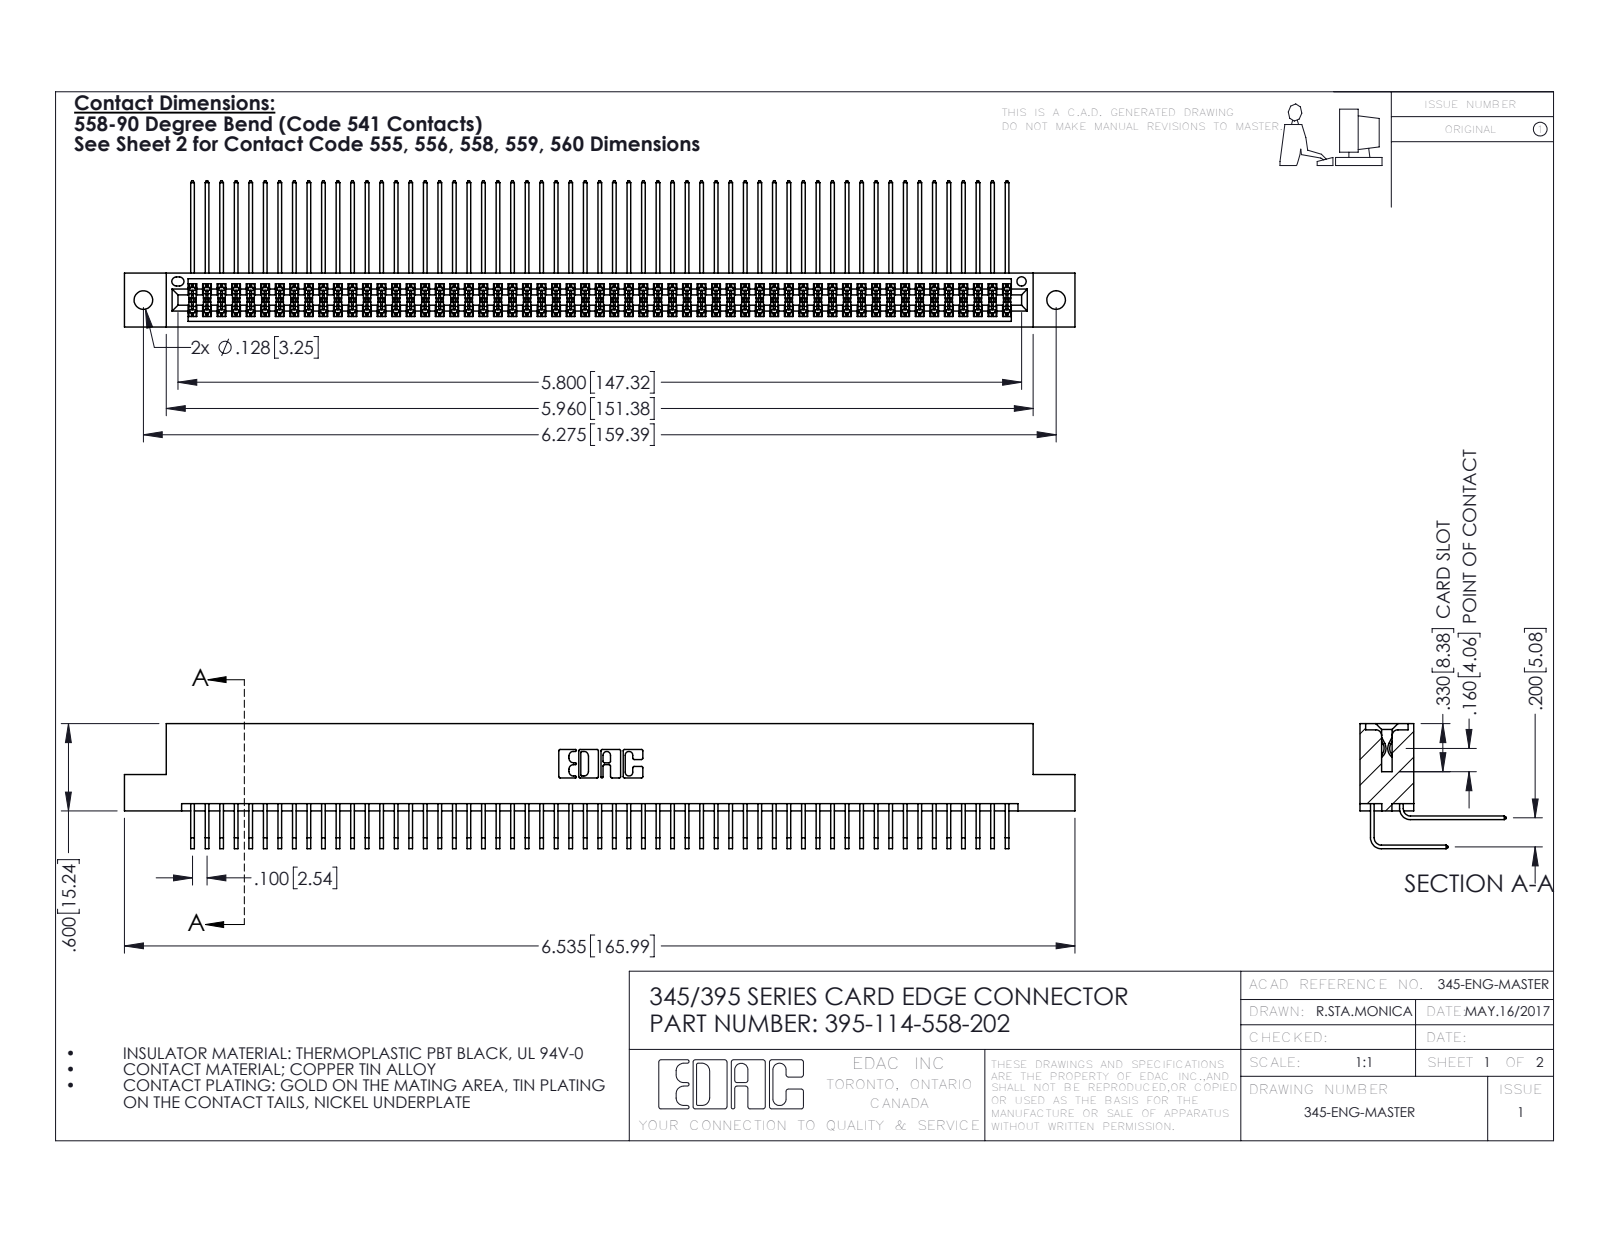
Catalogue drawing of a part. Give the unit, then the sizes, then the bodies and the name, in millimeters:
Units: millimetres
Overall size (bounding box): 166 × 25.5 × 21.8
Round holes (diameter × count): ⌀3.3 ×2, ⌀1.6 ×1
Partial cylindrical surfaces — rounded edges, fillets, slot ends (radius × count): R0.2 ×172, R0.3 ×22, R0.2 ×6, R0.8 ×6, R0.7 ×3, R0.4 ×2, R0.5 ×2, R0.6 ×2
Main face-to-face distances: 1.8, 7.6, 5.1, 9.4, 2.5, 6.9, 0.6, 5.7, 0.6, 4.4
Hole centre spacings: 6.9, 153.4, 159.4
Volume: 16 880 mm³ · Surface area: 28 070 mm²
Bodies: 115 solids, 6054 faces (4070 planar, 1984 cylindrical, 0 other)
Part name (STEP PRODUCT): 345 Part_Flush Mounting Lugs - 0.128 Dia; 345-292-001_558 Tail - 2; 395-114-558-202; 345-292-001_558 559 Tail - 1
STEP written by: SolidWorks 2016 (CONFIG_CONTROL_DESIGN)
